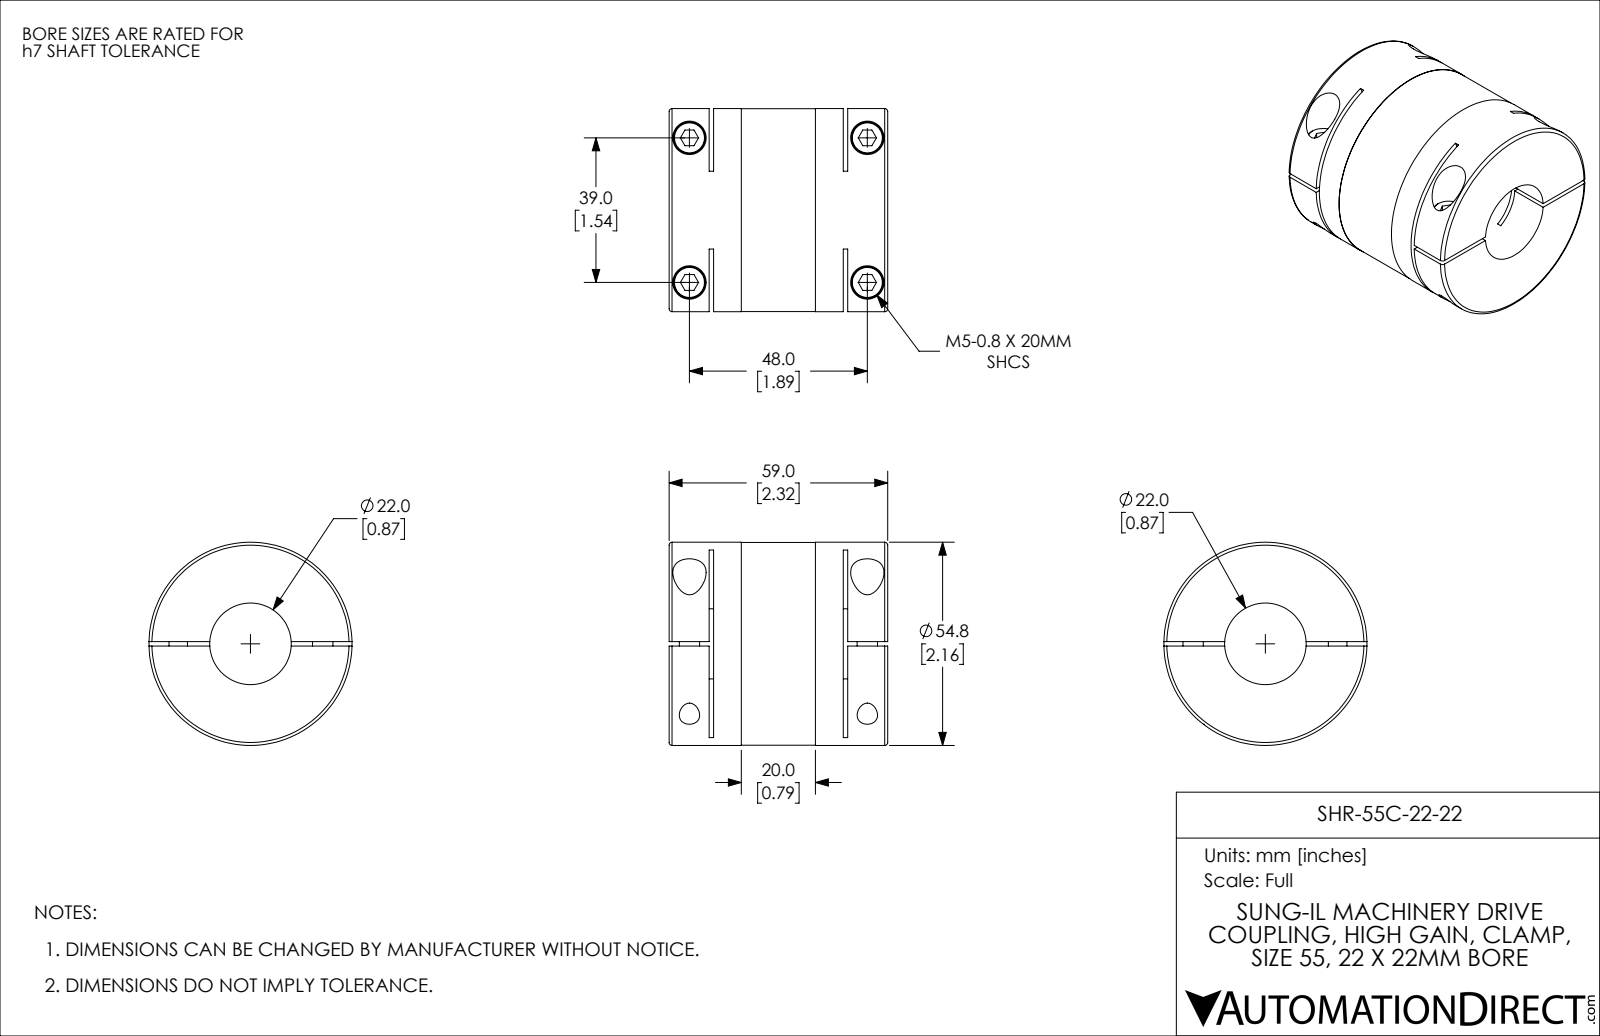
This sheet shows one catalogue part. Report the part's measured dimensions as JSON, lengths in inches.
{"part_name": "SHR-55C-22-22", "step_written_by": "SolidWorks 2021 (CONFIG_CONTROL_DESIGN)", "units": "inches", "bodies": {"solids": 1, "faces": 144, "planar": 70, "cylindrical": 58, "other": 16}, "overall_size": [2.323, 2.157, 2.157], "volume_in3": 6.591, "surface_area_in2": 44.1, "round_holes": [[0.217, 4], [0.354, 4], [0.866, 1], [0.945, 1]], "round_bosses_or_shafts": [[0.335, 4], [0.197, 2], [2.157, 1], [2.154, 1]], "partial_cylinders_radius": [[2.362, 2]], "face_to_face_distances": [0.047, 0.472, 1.85, 0.425, 1.898, 1.425, 2.323, 1.378, 1.472, 0.768], "hole_center_spacings": [1.535, 1.89, 2.435]}
